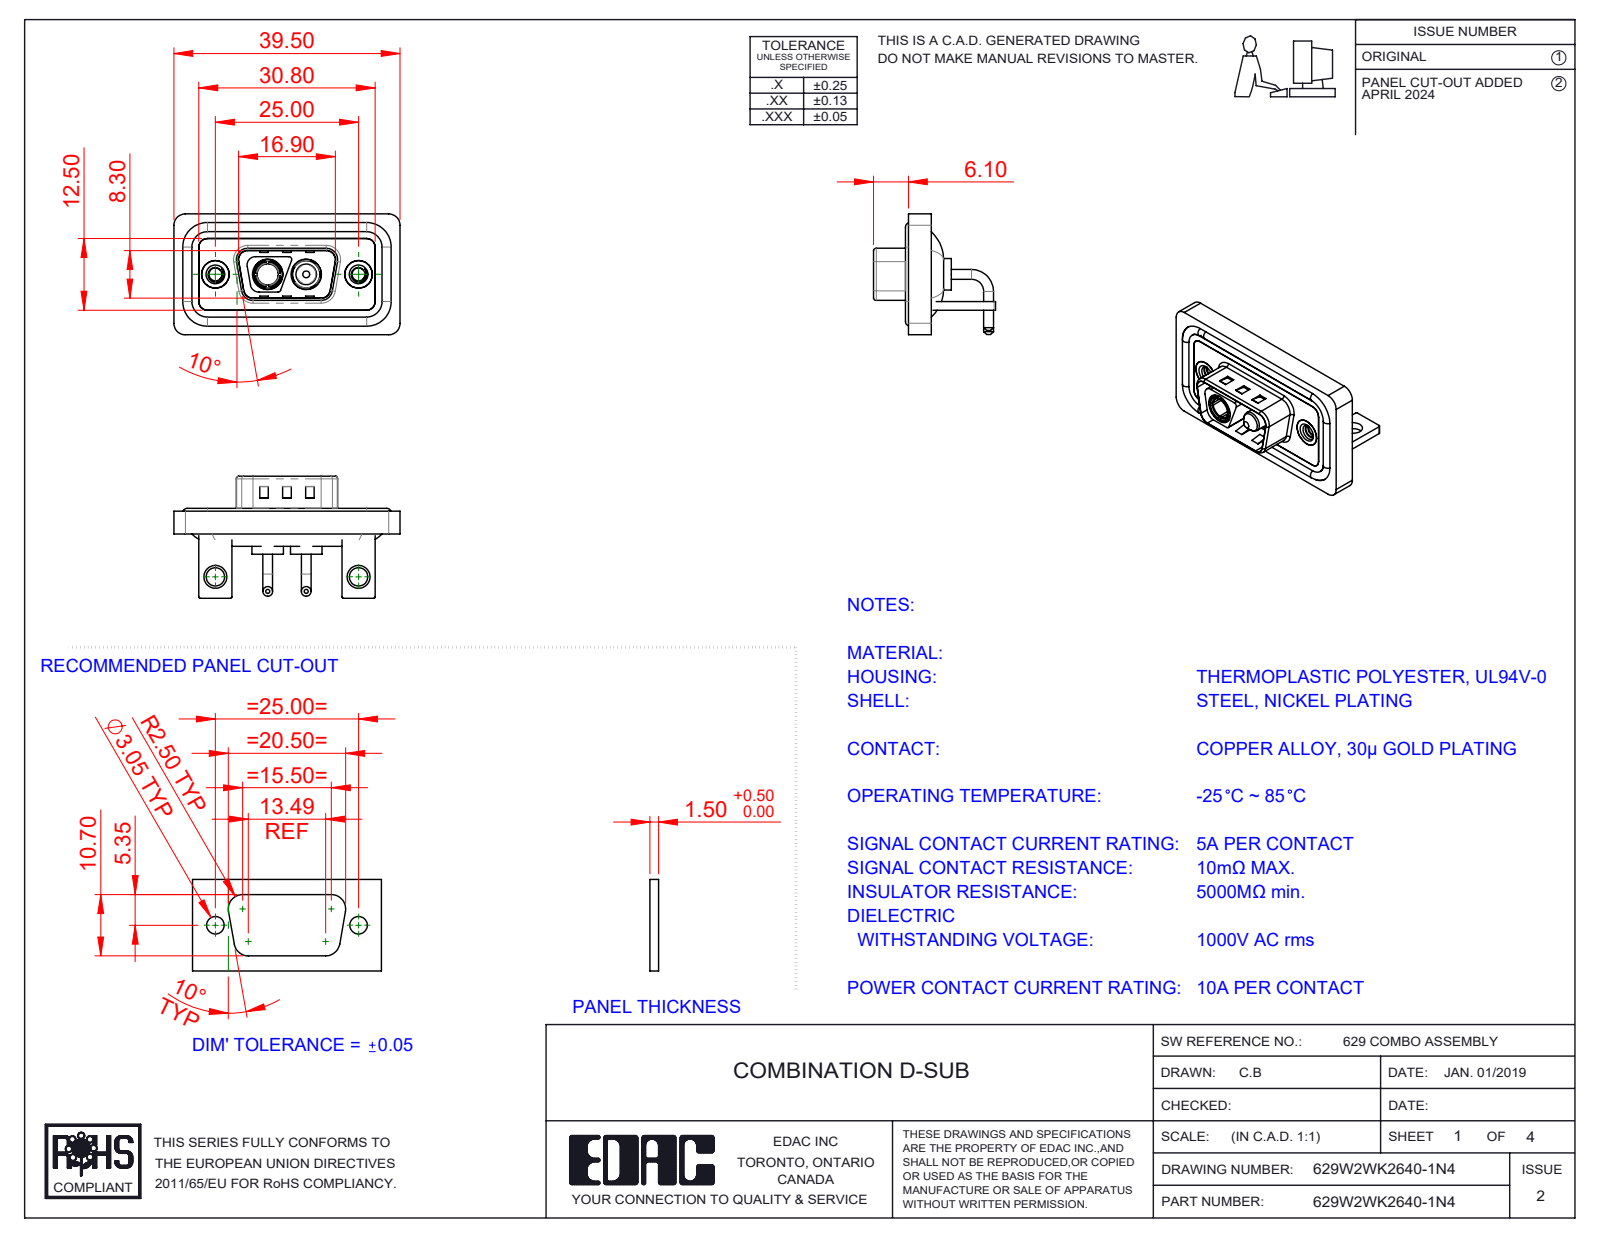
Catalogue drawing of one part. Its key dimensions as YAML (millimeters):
part_name: "629Combo Threaded Rivet_3; 629Combo Shell Rear_09 Contacts; 629Combo Stabilizer Bracket; Power Pin_10A RA (+5 more)"
step_written_by: "SolidWorks 2023 (CONFIG_CONTROL_DESIGN)"
units: millimeters
bodies: {solids: 13, faces: 582, planar: 209, cylindrical: 249, other: 124}
overall_size: [39.5, 21.3, 21.1]
volume: 4841
surface_area: 8015
round_holes:
  - {diameter: 2.26, count: 2}
  - {diameter: 3.2, count: 2}
  - {diameter: 4, count: 2}
  - {diameter: 4.8, count: 2}
  - {diameter: 4.85, count: 2}
  - {diameter: 5, count: 2}
  - {diameter: 5.3, count: 2}
  - {diameter: 3.7, count: 1}
round_bosses_or_shafts:
  - {diameter: 1.7, count: 4}
  - {diameter: 1.6, count: 4}
  - {diameter: 5.5, count: 2}
  - {diameter: 5.2, count: 2}
  - {diameter: 4.9, count: 2}
  - {diameter: 4.75, count: 2}
  - {diameter: 3.75, count: 2}
  - {diameter: 4.96, count: 1}
partial_cylinders:
  - {radius: 1.5, count: 20}
  - {radius: 2, count: 19}
  - {radius: 0.25, count: 16}
  - {radius: 0.5, count: 11}
  - {radius: 1.6, count: 8}
  - {radius: 0.6, count: 4}
  - {radius: 0.65, count: 4}
  - {radius: 0.9, count: 4}
face_to_face_distances: [0.4, 1.5, 2.9, 0.8, 1.1, 1.2, 2.1, 1.6, 3.7, 2.5]
hole_center_spacings: [9.14, 15.86, 25, 6.72]
